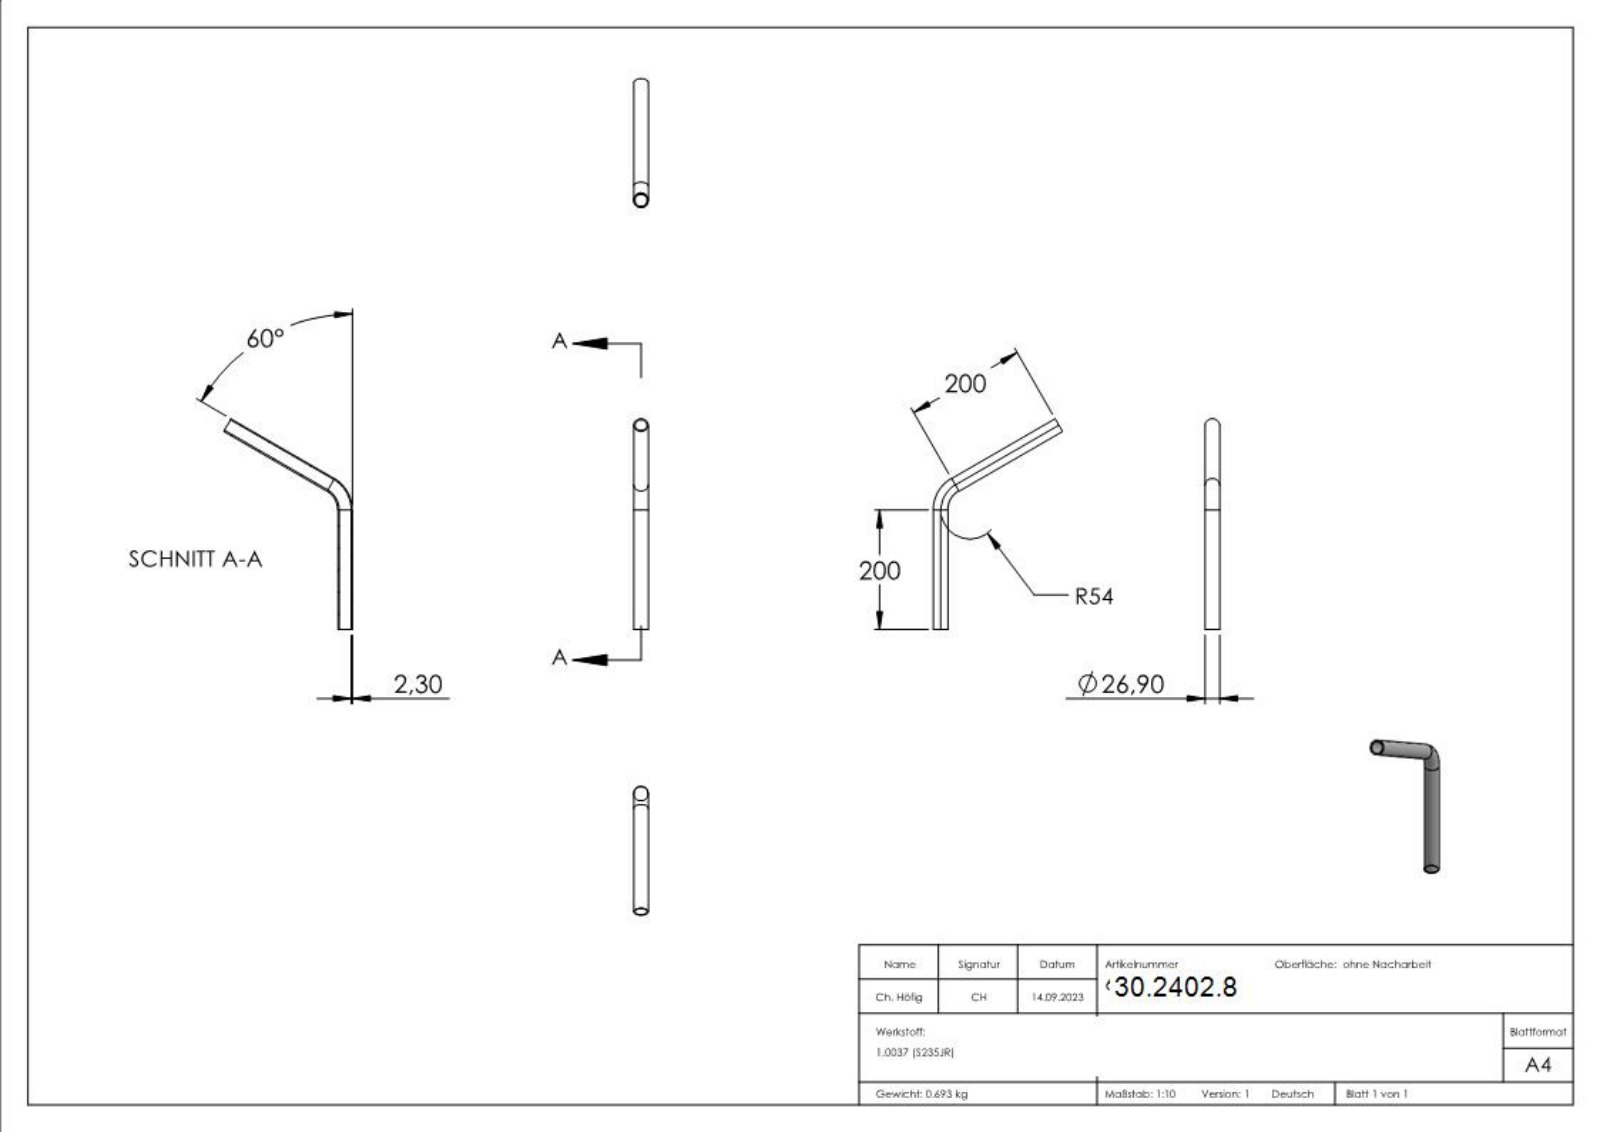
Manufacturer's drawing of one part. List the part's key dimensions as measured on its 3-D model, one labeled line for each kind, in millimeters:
Part name (STEP PRODUCT): 6965-060
STEP written by: SolidWorks 2018 (CONFIG_CONTROL_DESIGN)
Units: millimetres
Bodies: 1 solid, 219 faces (103 planar, 4 cylindrical, 112 other)
Overall size (bounding box): 391 × 239.19 × 26.9
Volume: 88 876 mm³ · Surface area: 77 642 mm²
Round holes (diameter × count): ⌀22.3 ×2
Round bosses / shafts (diameter × count): ⌀26.9 ×2
Main face-to-face distances: 0.53, 0.58, 0.34, 0.39, 0.32, 0.48, 0.31, 0.35, 0.4, 0.54
